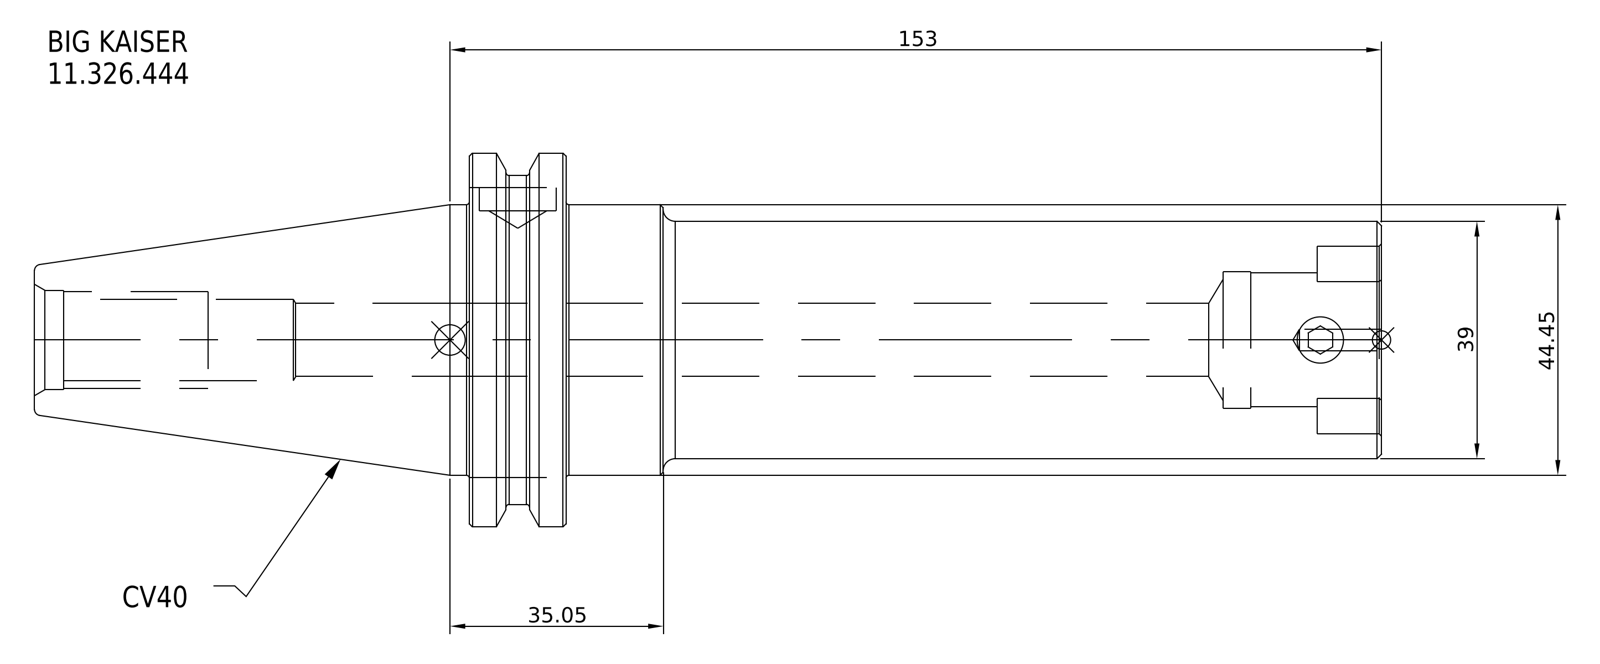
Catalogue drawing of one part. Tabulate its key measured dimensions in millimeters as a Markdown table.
| quantity | value |
| --- | --- |
| part name | 11_326_444 |
| STEP written by | SolidWorks 2021 (CONFIG_CONTROL_DESIGN) |
| units | millimeters |
| bodies | 1 solid, 27 faces (7 planar, 12 cylindrical, 8 other) |
| overall size | 221.25 × 63.5 × 63.5 |
| volume | 283 153 mm³ |
| surface area | 33 706 mm² |
| round bosses / shafts (diameter × count) | 63.5 × 1, 56.36 × 1, 44.45 × 1, 39 × 1 |
| main face-to-face distances | 15.88, 133.95, 149.83, 221.25, 87.3, 71.42, 139.95, 6, 9.88, 81.3 |
